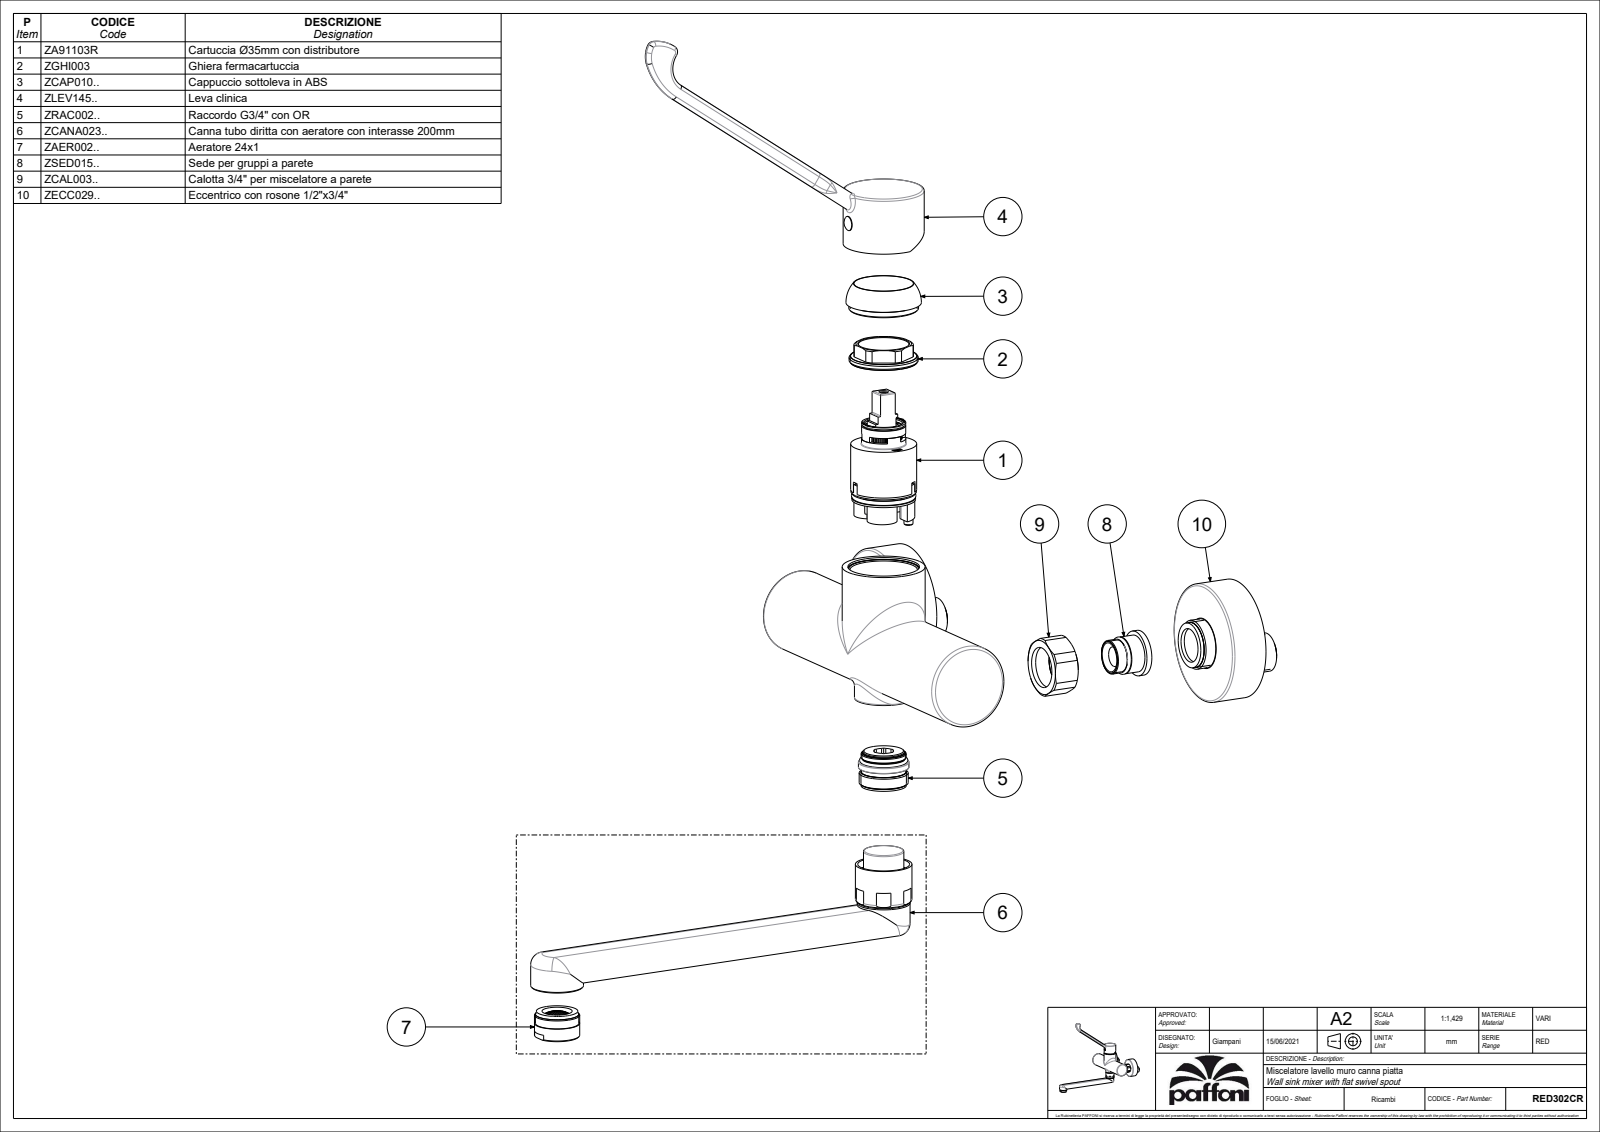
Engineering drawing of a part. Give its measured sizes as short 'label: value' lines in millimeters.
name: RED302CR
written by: CREO PARAMETRIC BY PTC INC, 2020044 (CONFIG_CONTROL_DESIGN)
unit: mm
bodies: 3 solids, 3016 faces (2184 planar, 471 cylindrical, 361 other)
size: 271.5 × 252.78 × 213.5
volume: 223 108 mm³; area: 176 538 mm²
holes: 3× ⌀9, 3× ⌀12, 2× ⌀4, 2× ⌀7, 2× ⌀8, 2× ⌀10.5, 2× ⌀18, 2× ⌀20.5, 2× ⌀21.5, 2× ⌀24.1, 2× ⌀25, 2× ⌀26
bosses: 3× ⌀24, 2× ⌀63.5, 2× ⌀44, 2× ⌀28, 2× ⌀27, 2× ⌀19.7, 2× ⌀9, 1× ⌀43
rounds: 83× R0.5, 11× R0.15, 9× R0.3, 6× R7, 4× R1, 4× R2, 2× R7.95, 2× R8
face distances: 1, 15, 0.6, 16, 14, 20.5, 3, 68.5, 112.5, 19.75
hole spacings: 0.71, 8.51, 8.6, 13.04, 13.21, 13.51, 89.86, 96.86
